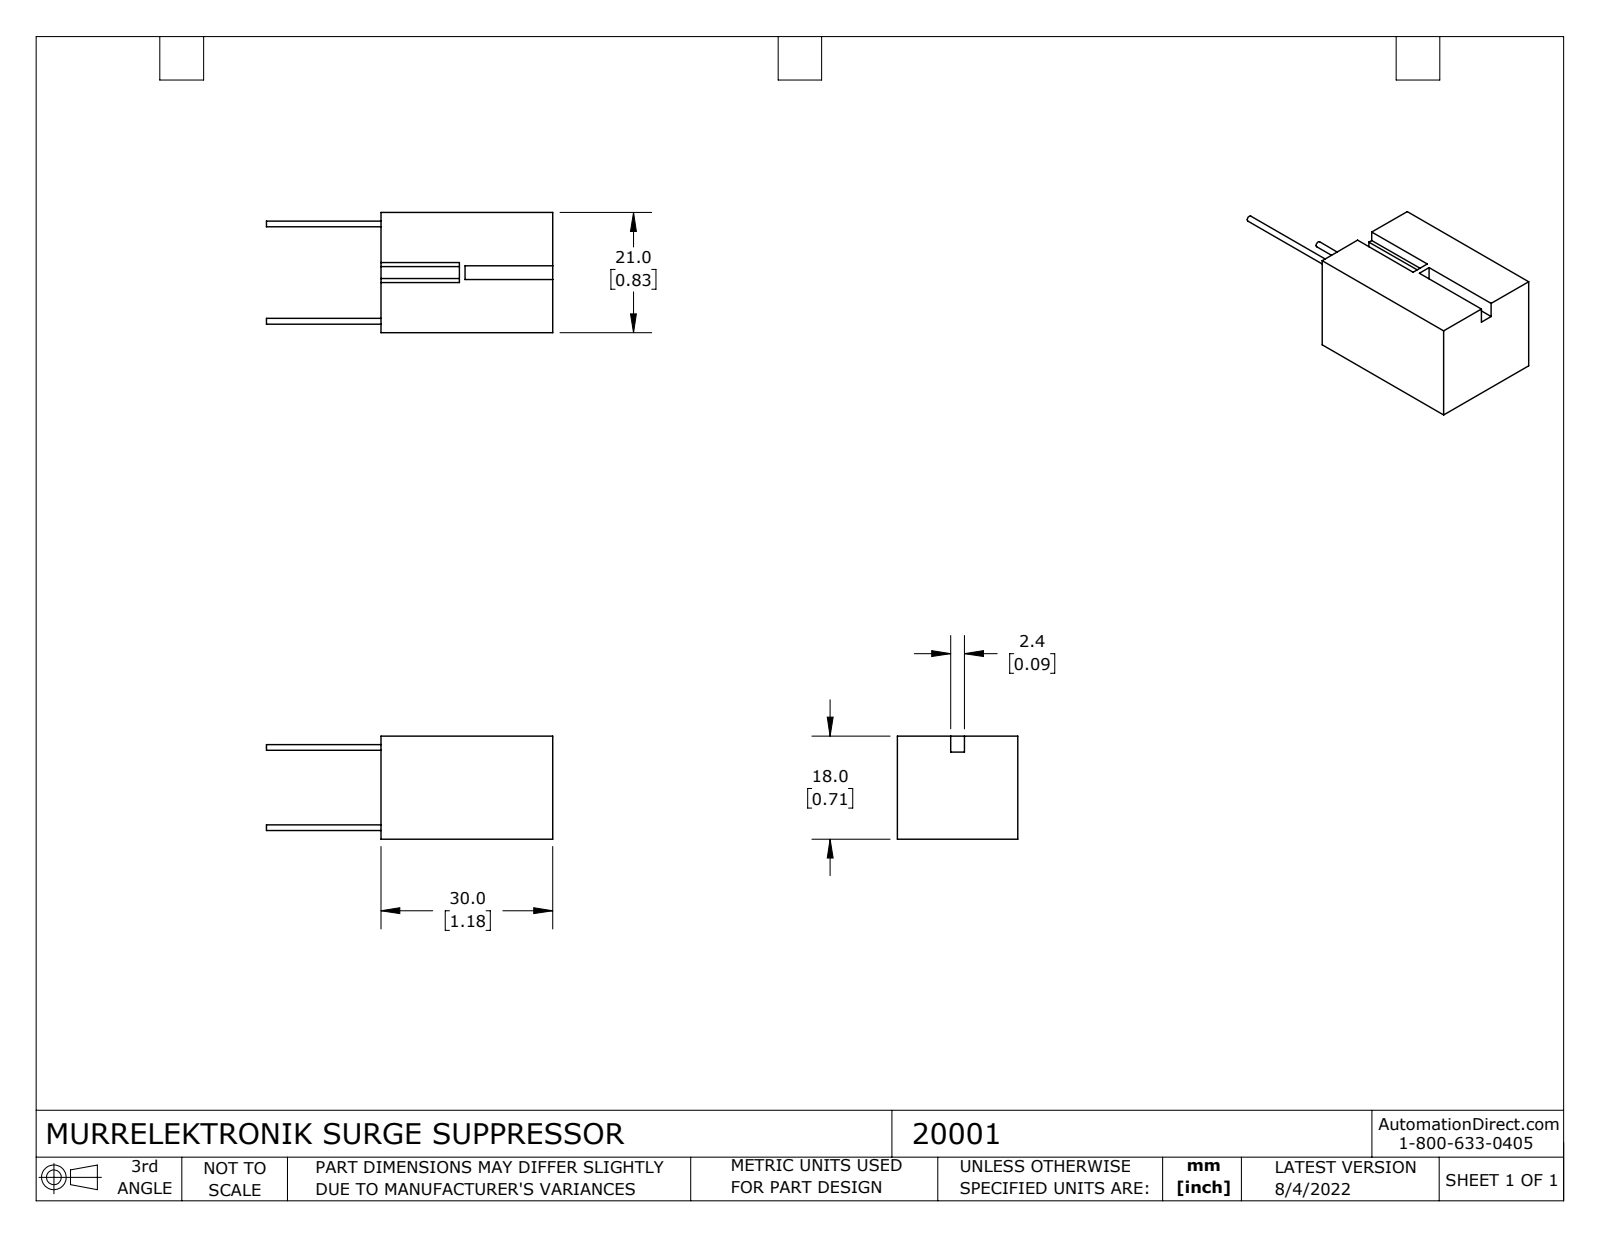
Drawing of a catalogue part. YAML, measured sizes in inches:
part_name: "20001"
step_written_by: "SolidWorks 2021 (CONFIG_CONTROL_DESIGN)"
units: inches
bodies: {solids: 1, faces: 24, planar: 20, cylindrical: 4, other: 0}
overall_size: [1.969, 0.827, 0.709]
volume: 0.681
surface_area: 5.245
round_bosses_or_shafts:
  - {diameter: 0.039, count: 2}
face_to_face_distances: [0.709, 0.827, 1.181, 0.11, 0.366, 0.461, 0.598, 0.344, 0.482, 0.022]
